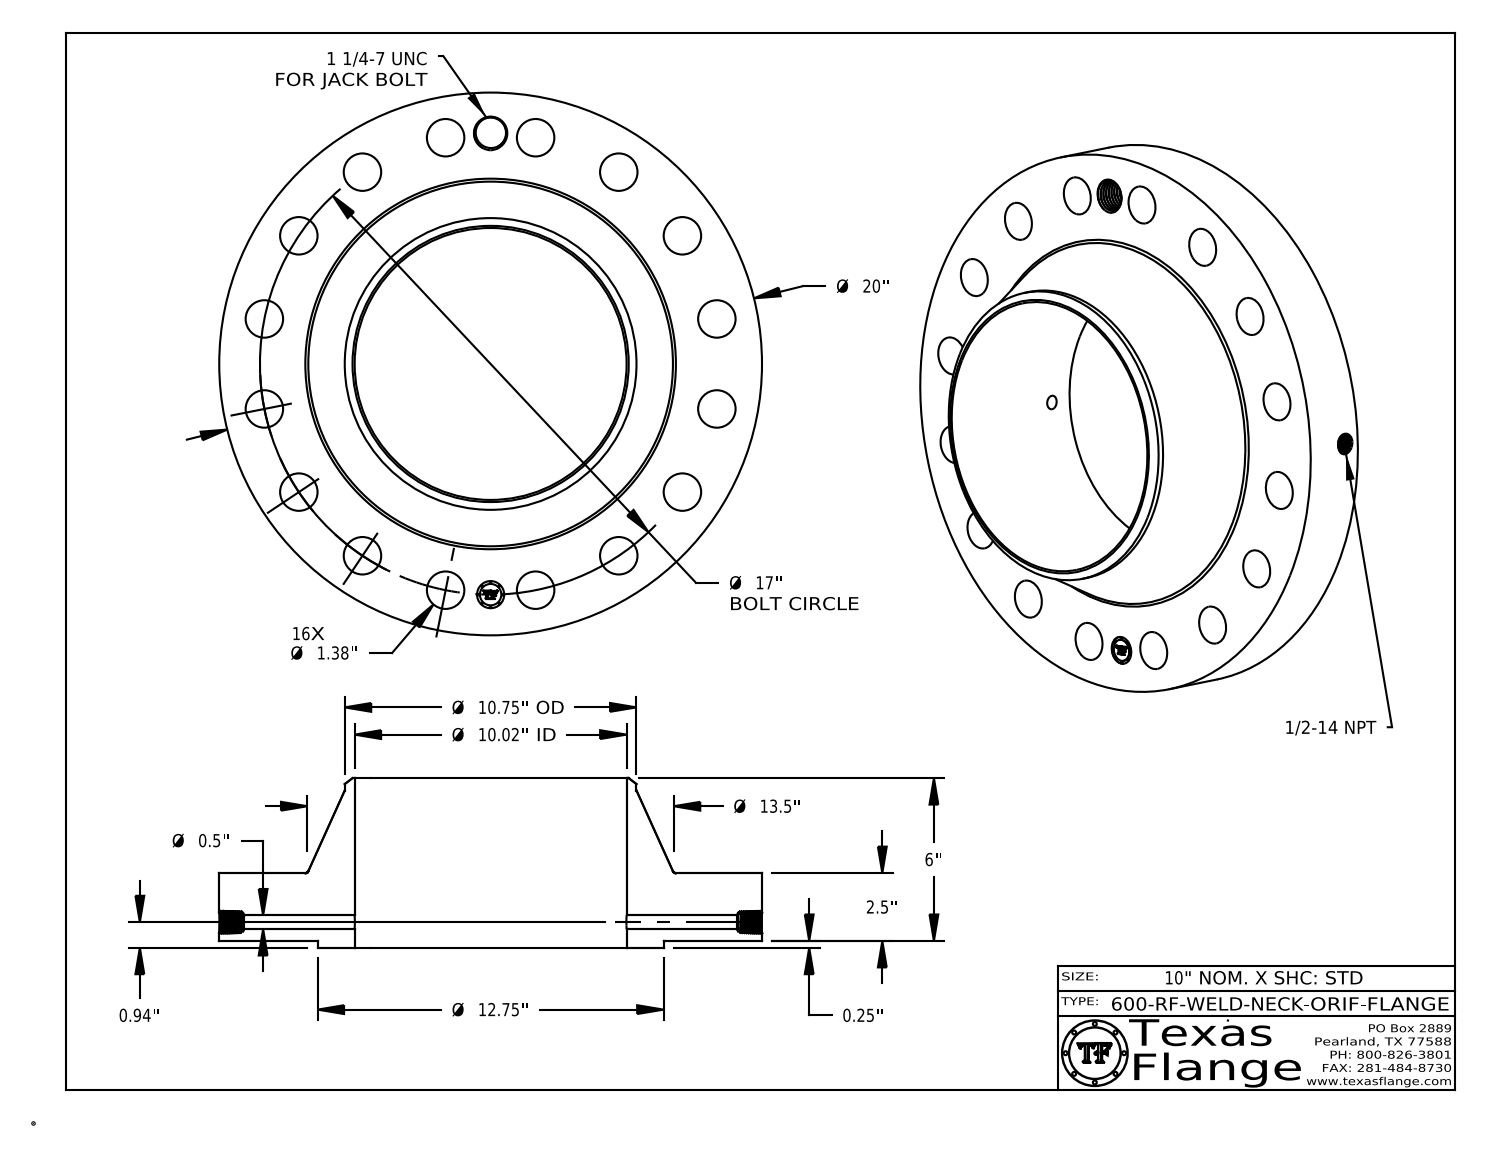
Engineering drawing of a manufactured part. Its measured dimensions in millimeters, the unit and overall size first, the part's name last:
Units: millimetres
Overall size (bounding box): 508 × 508 × 158.8
Round holes (diameter × count): ⌀35.1 ×16, ⌀12.7 ×1, ⌀17.1 ×1, ⌀25.4 ×1, ⌀28.2 ×1, ⌀254.5 ×1
Round bosses / shafts (diameter × count): ⌀1.5 ×8, ⌀508 ×1, ⌀323.9 ×1, ⌀273.1 ×1, ⌀20 ×1
Main face-to-face distances: 63.5, 6.4, 69.9, 158.8, 152.4, 88.9, 69.5, 63.1, 0.4, 89.3
Hole centre spacings: 215.9, 305.3, 398.9, 423.5, 84.3, 239.9, 359, 431.8
Volume: 10 700 000 mm³ · Surface area: 693 500 mm²
Bodies: 1 solid, 802 faces (369 planar, 115 cylindrical, 318 other)
Part name (STEP PRODUCT): 600-RF-WELD-NECK
STEP written by: CATIA V5 STEP AP214 (AUTOMOTIVE_DESIGN)
